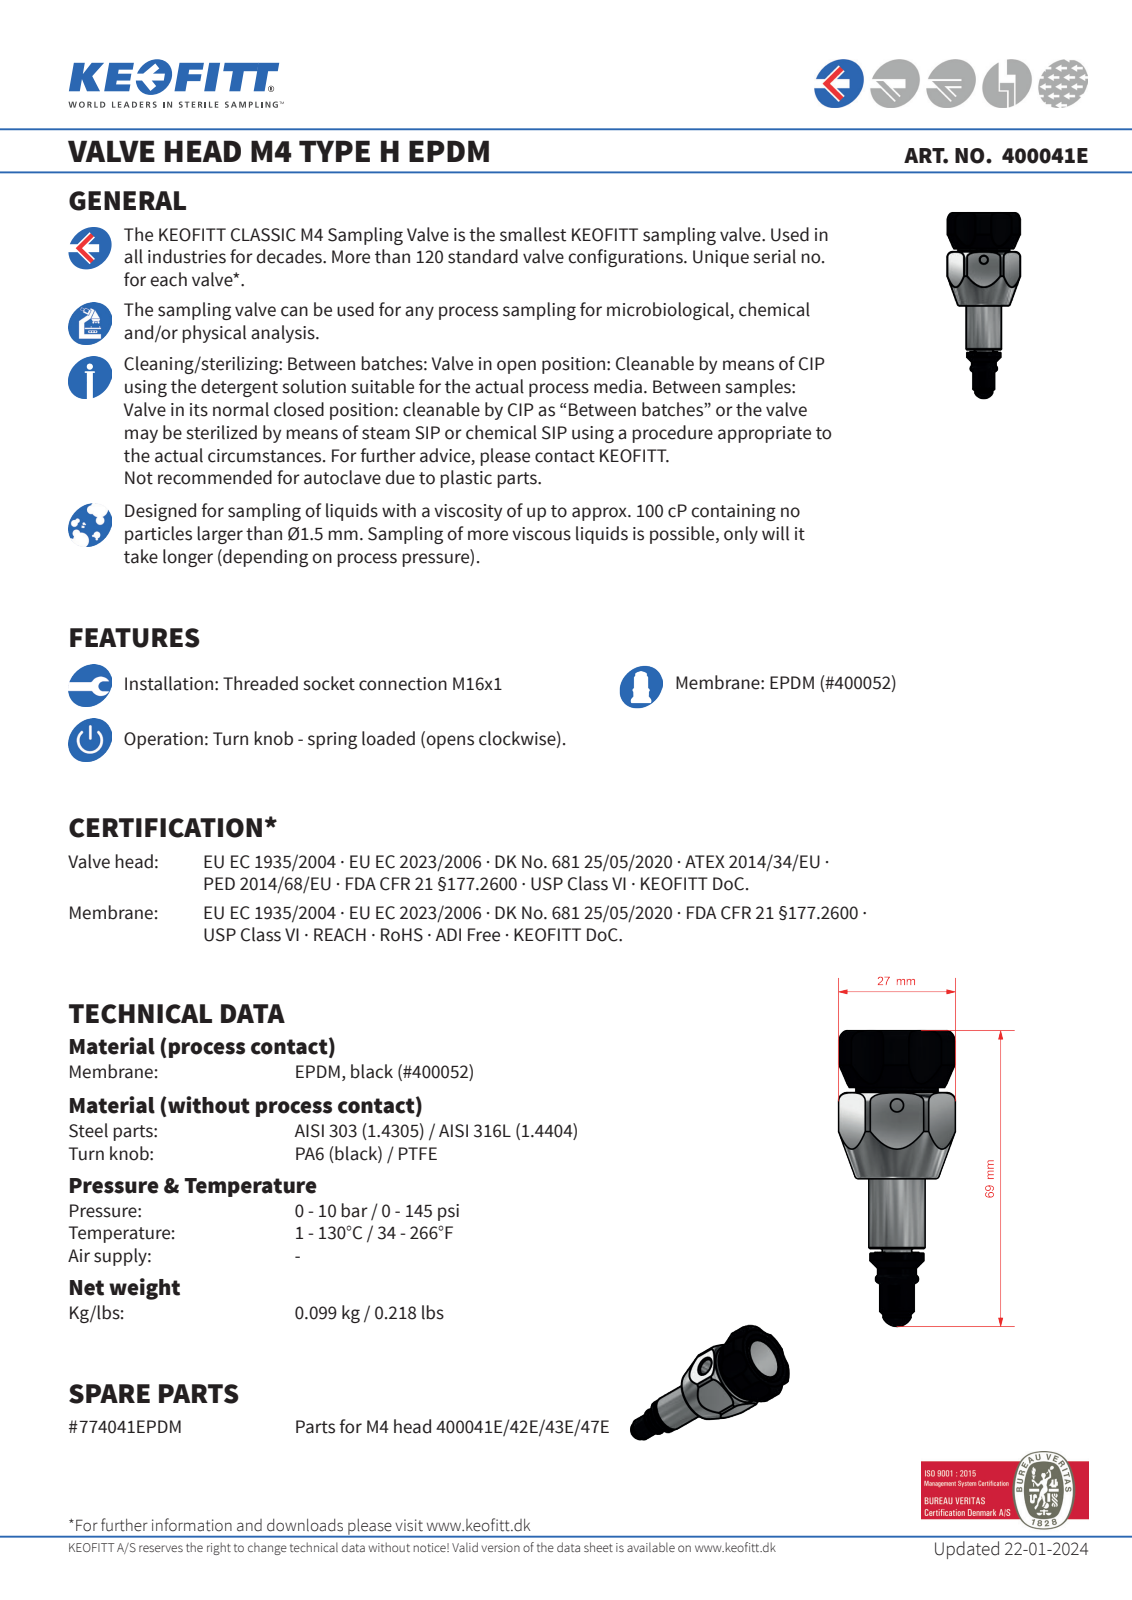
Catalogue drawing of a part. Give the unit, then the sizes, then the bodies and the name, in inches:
Units: inches
Overall size (bounding box): 2.658 × 1.102 × 1.062
Round holes (diameter × count): ⌀0.12 ×1, ⌀0.24 ×1, ⌀0.402 ×1, ⌀0.455 ×1, ⌀0.587 ×1, ⌀0.591 ×1, ⌀0.65 ×1
Round bosses / shafts (diameter × count): ⌀0.748 ×1, ⌀0.63 ×1, ⌀0.512 ×1, ⌀0.492 ×1, ⌀0.453 ×1, ⌀0.431 ×1, ⌀0.394 ×1, ⌀0.354 ×1
Partial cylindrical surfaces — rounded edges, fillets, slot ends (radius × count): R0.236 ×6, R0.069 ×1, R0.16 ×1, R0.376 ×1, R0.531 ×1, R0.551 ×1
Main face-to-face distances: 0.945, 0.543, 0.563, 0.02, 0.012, 0.531, 0.551, 0.044, 0.021, 0.031
Hole centre spacings: 0.079
Volume: 1.119 in³ · Surface area: 10.87 in²
Bodies: 1 solid, 93 faces (23 planar, 41 cylindrical, 29 other)
STEP written by: Autodesk Inventor 2008 (AUTOMOTIVE_DESIGN)
